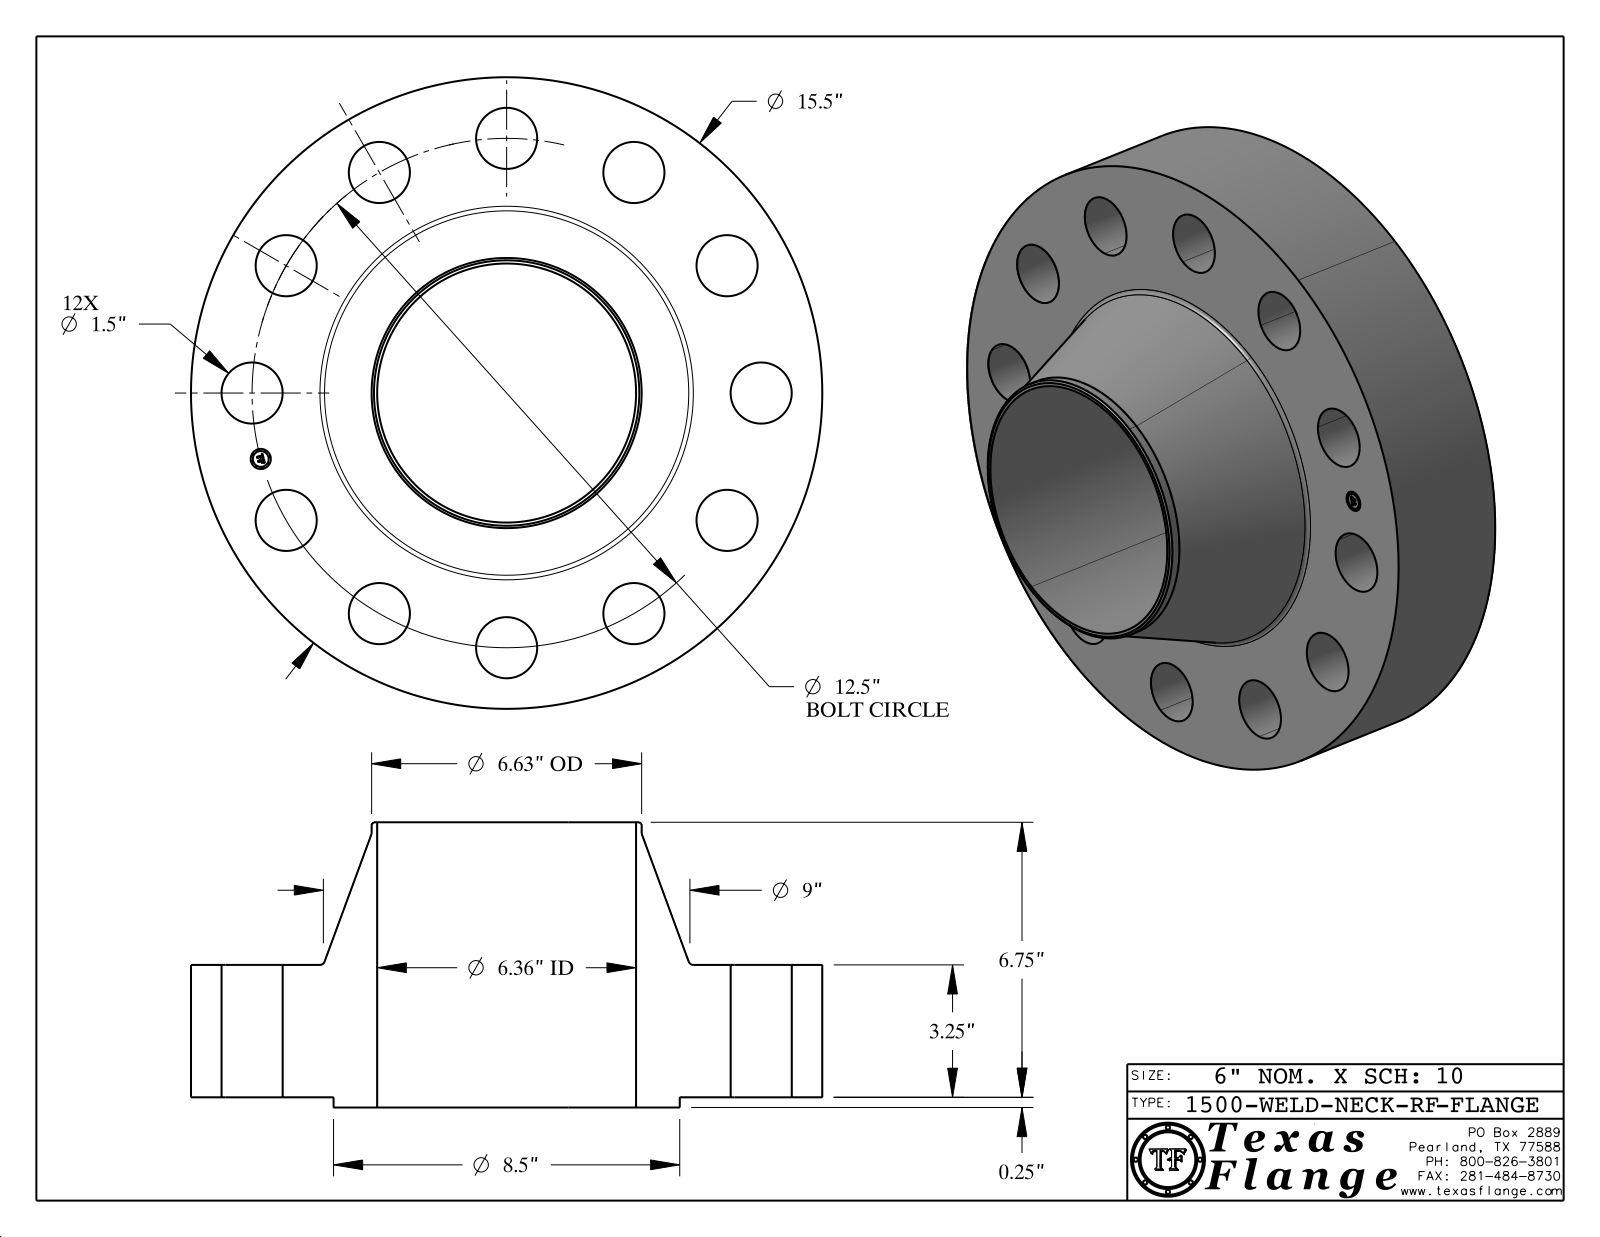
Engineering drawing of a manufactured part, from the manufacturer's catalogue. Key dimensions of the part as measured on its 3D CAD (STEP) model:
Part name (STEP PRODUCT): 1500-WELD-NECK-RF
STEP written by: CATIA V5 STEP AP214 (AUTOMOTIVE_DESIGN)
Units: inches
Bodies: 1 solid, 427 faces (369 planar, 52 cylindrical, 6 other)
Overall size (bounding box): 15.5 × 15.5 × 7
Volume: 501.6 in³ · Surface area: 819.9 in²
Round holes (diameter × count): ⌀1.5 ×12, ⌀0.495 ×1, ⌀6.357 ×1
Round bosses / shafts (diameter × count): ⌀0.03 ×8, ⌀15.5 ×1, ⌀8.5 ×1, ⌀6.63 ×1, ⌀0.39 ×1
Main face-to-face distances: 3.25, 3.5, 0.25, 7, 6.75, 3.485, 3.235, 0.015, 3.515, 0.148
Hole centre spacings: 6.25, 8.839, 3.235, 10.826, 12.074, 12.5, 3.235, 6.25
